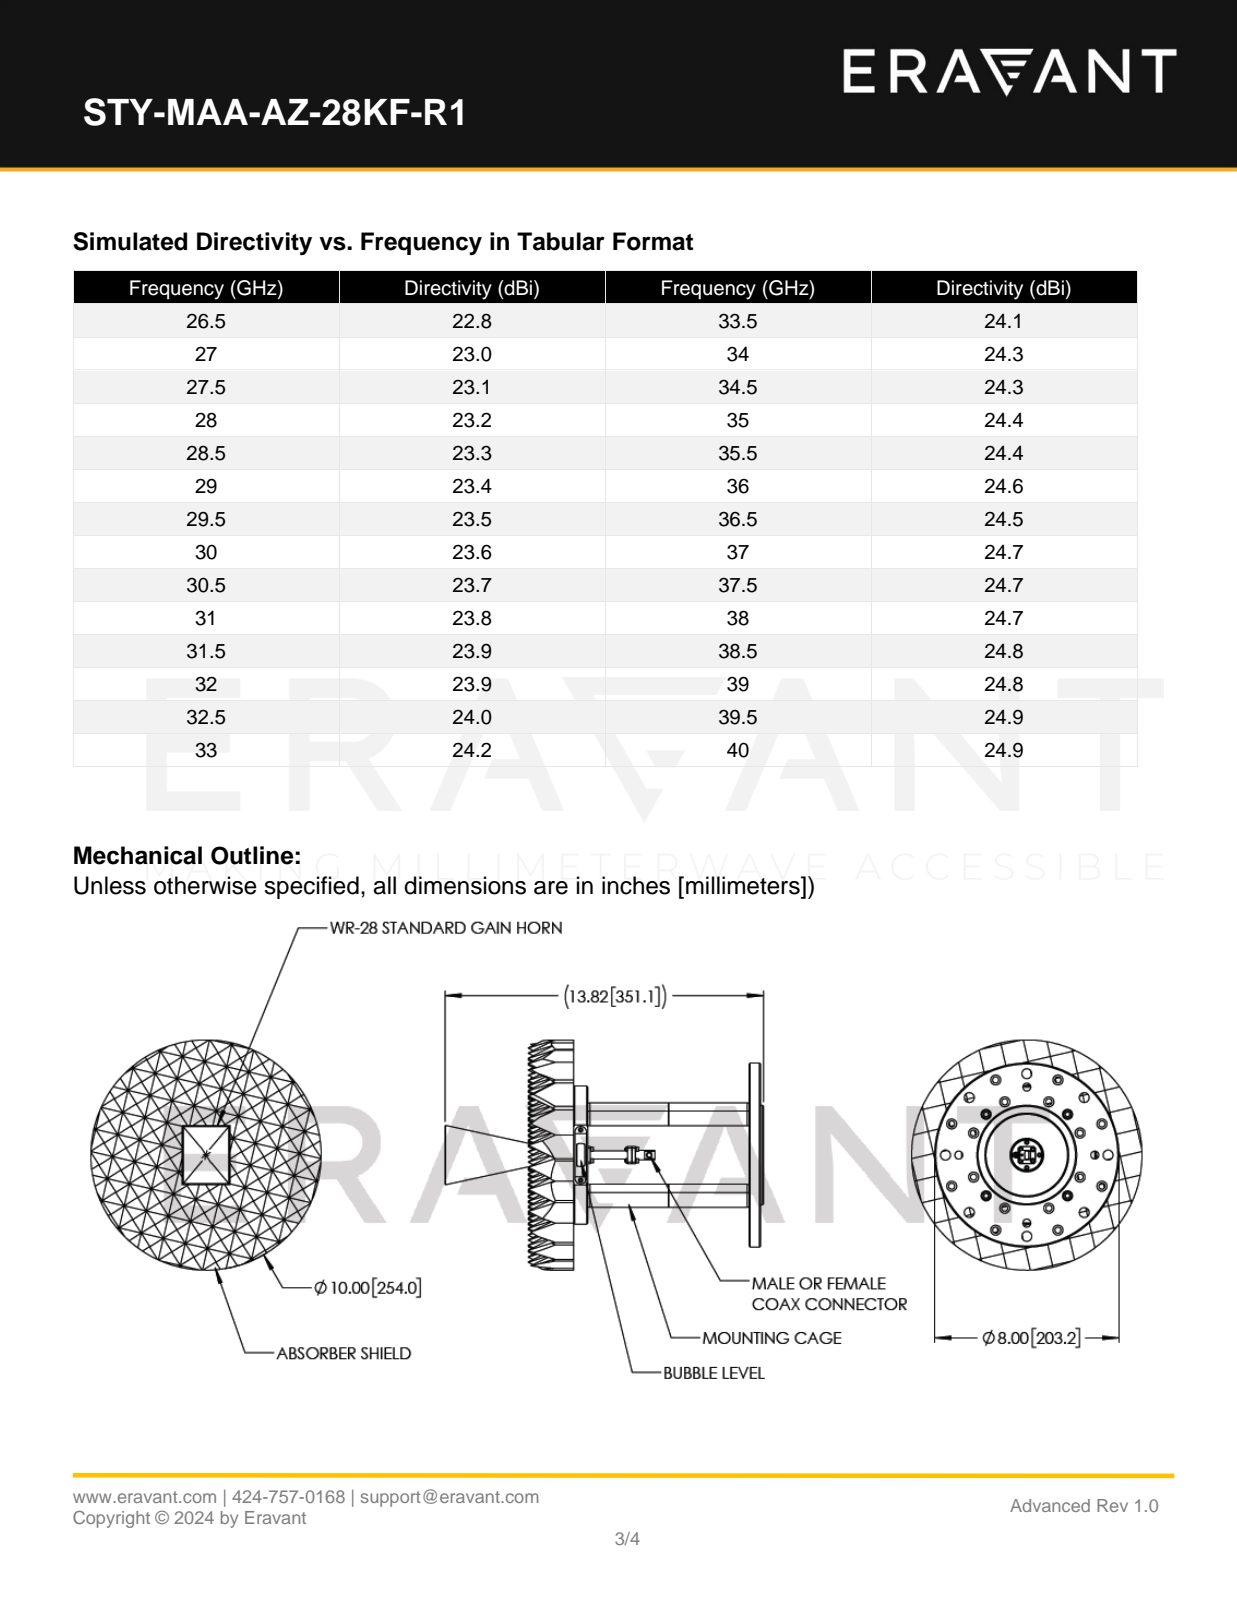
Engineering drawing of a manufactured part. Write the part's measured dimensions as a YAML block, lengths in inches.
part_name: "STY-MAA-AZ-34KF-R1"
step_written_by: "SolidWorks 2021 (CONFIG_CONTROL_DESIGN)"
units: inches
bodies: {solids: 88, faces: 1857, planar: 731, cylindrical: 459, other: 667}
overall_size: [14.917, 10, 10]
volume: 169.5
surface_area: 832.7
round_holes:
  - {diameter: 0.266, count: 20}
  - {diameter: 0.437, count: 16}
  - {diameter: 0.433, count: 8}
  - {diameter: 0.12, count: 4}
  - {diameter: 0.348, count: 4}
  - {diameter: 0.75, count: 4}
  - {diameter: 0.089, count: 2}
  - {diameter: 0.125, count: 2}
  - {diameter: 0.182, count: 1}
  - {diameter: 1.55, count: 1}
  - {diameter: 3.543, count: 1}
round_bosses_or_shafts:
  - {diameter: 0.21, count: 5}
  - {diameter: 1, count: 4}
  - {diameter: 0.437, count: 4}
  - {diameter: 0.183, count: 4}
  - {diameter: 0.112, count: 4}
  - {diameter: 0.08, count: 4}
  - {diameter: 10, count: 1}
  - {diameter: 8, count: 1}
partial_cylinders:
  - {radius: 0.042, count: 4}
  - {radius: 0.106, count: 4}
  - {radius: 0.08, count: 2}
  - {radius: 0.25, count: 2}
  - {radius: 0.24, count: 1}
face_to_face_distances: [0.984, 1.969, 0.985, 1.969, 2.953, 2.953, 3.937, 0.984, 4.922, 3.937]
hole_center_spacings: [4.326, 5.585, 3.458, 5.046, 5.918, 1.551, 2.496, 3.53]
